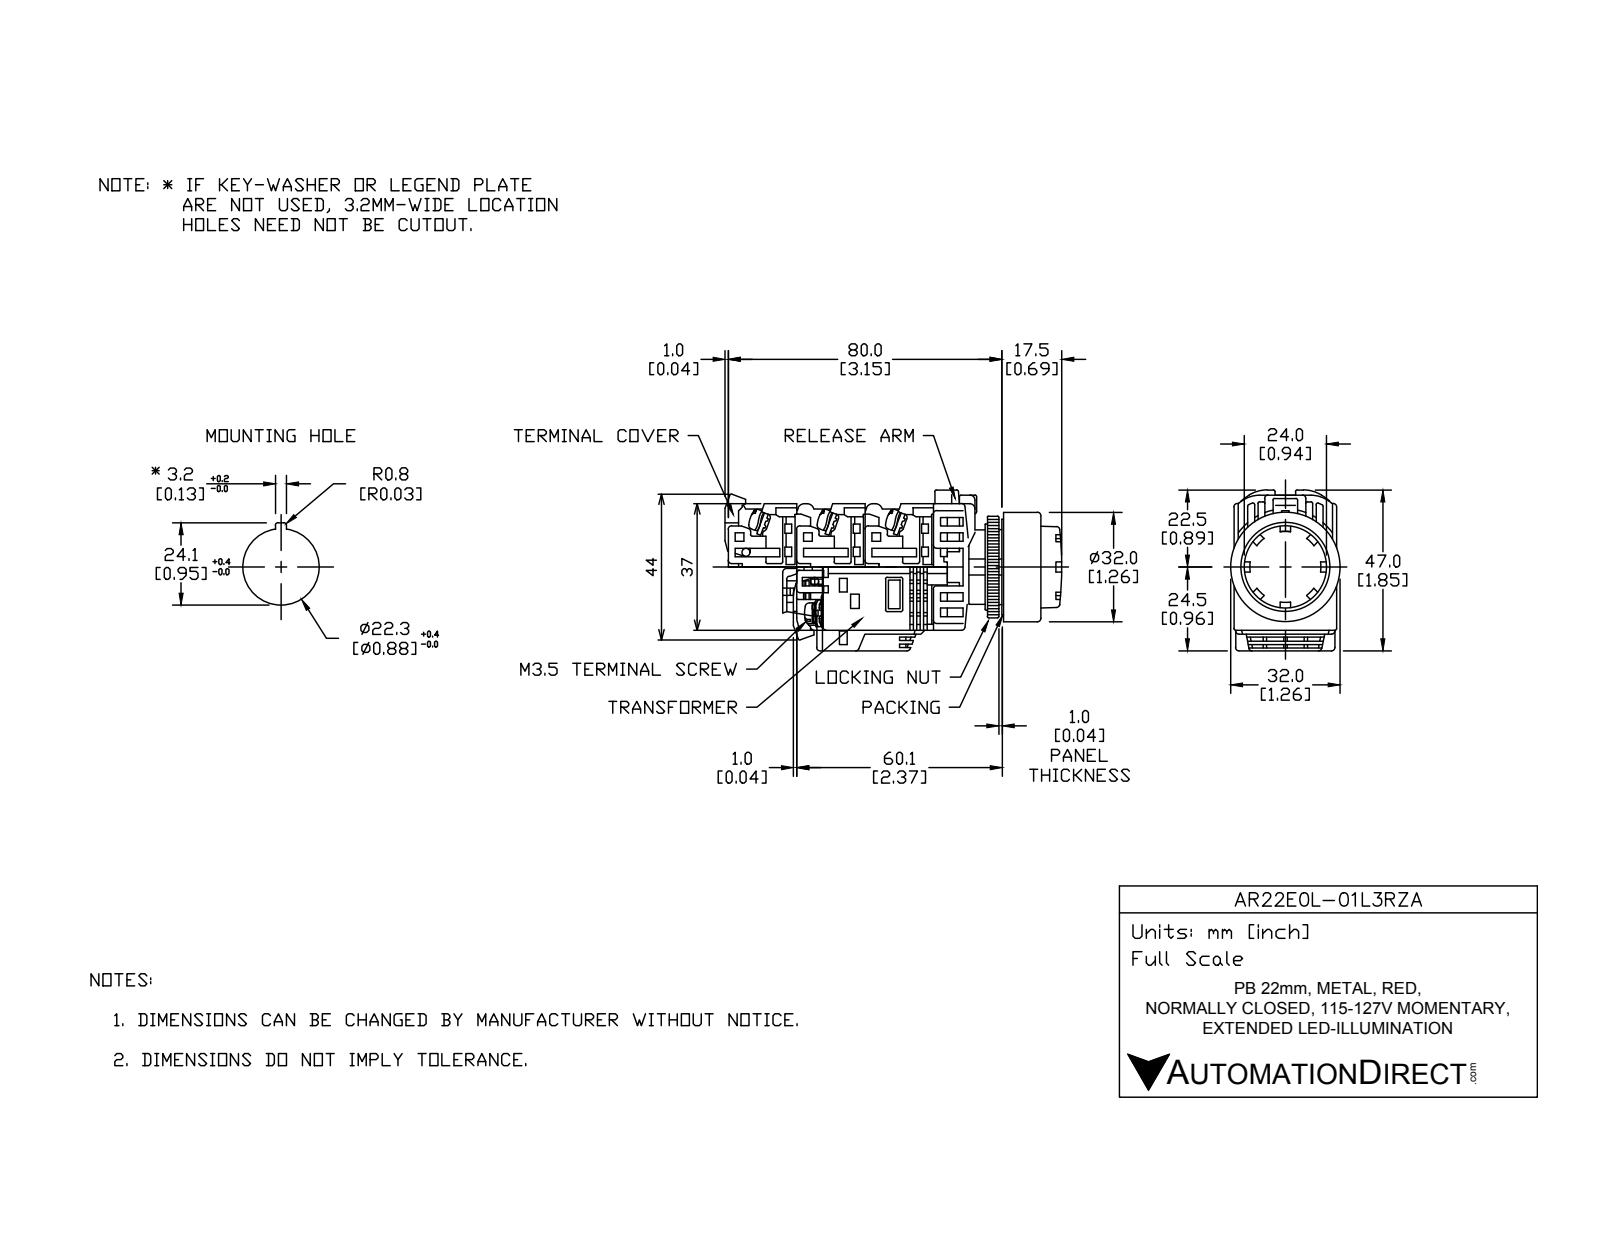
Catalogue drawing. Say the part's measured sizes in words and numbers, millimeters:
The part is named "AR22E0L-01L3RZA". Its 3-D file was written by "SolidWorks 2017 (AUTOMOTIVE_DESIGN)". It is 16 solids with 451 faces: 317 planar, 99 cylindrical and 35 other. Overall it measures 79.25 by 43.81 by 32 millimeters. Its volume is 50 413 cubic millimeters and its surface area 26 207 square millimeters. Round holes: 1 of diameter 21.8, 1 of diameter 22, 1 of diameter 25, 1 of diameter 31. Round bosses or shafts: 4 of diameter 5, 1 of diameter 32, 1 of diameter 30.5, 1 of diameter 29.8, 1 of diameter 24, 1 of diameter 23.8, 1 of diameter 21.75, 1 of diameter 17. Partial cylindrical surfaces (rounded edges, fillets, slot ends): 32 of radius 0.5, 8 of radius 1.75, 4 of radius 5, 2 of radius 4, 1 of radius 16.59, 1 of radius 17.59. The main face-to-face distances are 1, 18, 29, 20, 28.5, 3, 2, 21, 0.35, 7.5.
